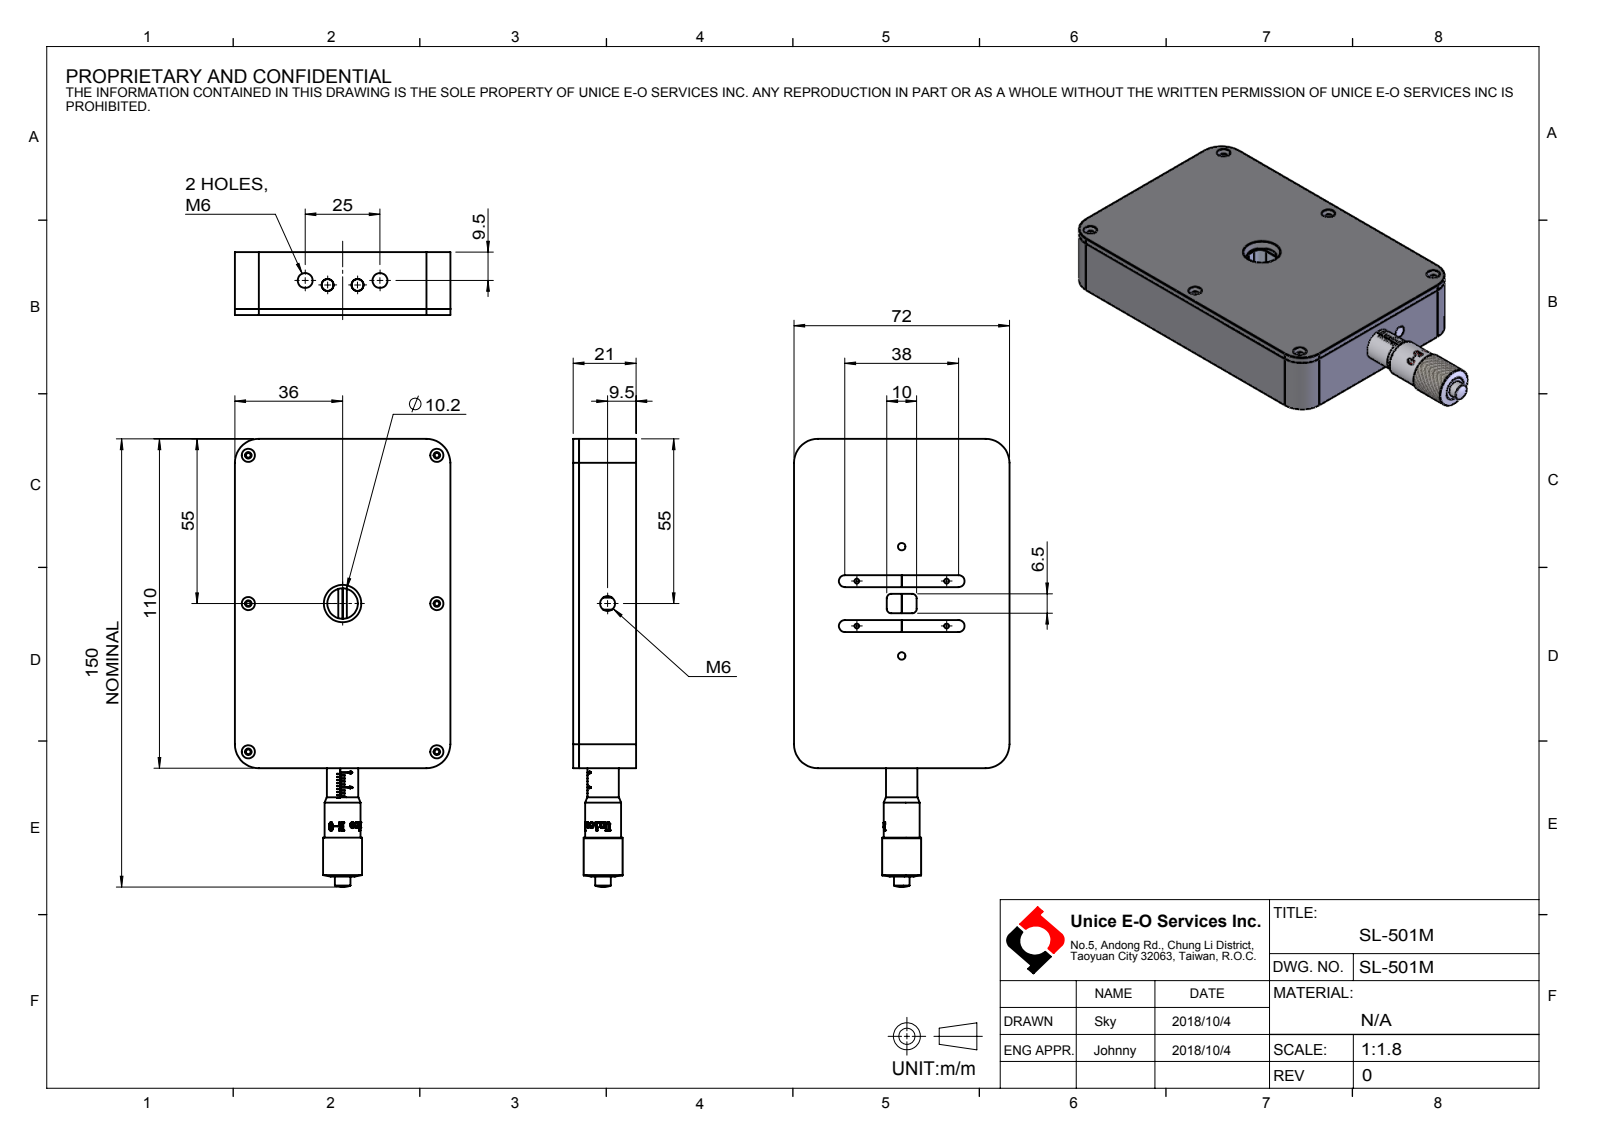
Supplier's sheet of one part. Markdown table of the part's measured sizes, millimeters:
| quantity | value |
| --- | --- |
| part name | SL-501M |
| STEP written by | SolidWorks 2016 (AUTOMOTIVE_DESIGN) |
| units | millimeters |
| bodies | 0 solids, 171 faces (62 planar, 74 cylindrical, 35 other) |
| overall size | 149.68 × 72 × 21 |
| round holes (diameter × count) | 2.2 × 6, 1.6 × 4, 5 × 3, 2.5 × 2, 10.6 × 1 |
| round bosses / shafts (diameter × count) | 13 × 1, 12 × 1, 10.5 × 1, 5.2 × 1 |
| partial cylindrical surfaces (radius × count) | 1.5 × 4, 2 × 4, 3 × 4, 8 × 4, 5.98 × 1 |
| main face-to-face distances | 2, 19, 21, 15, 4, 72, 6, 11, 110, 17 |
| hole center spacings | 49.5, 80.12, 63, 12.59, 36.03, 36.79, 43.85, 44.9 |
